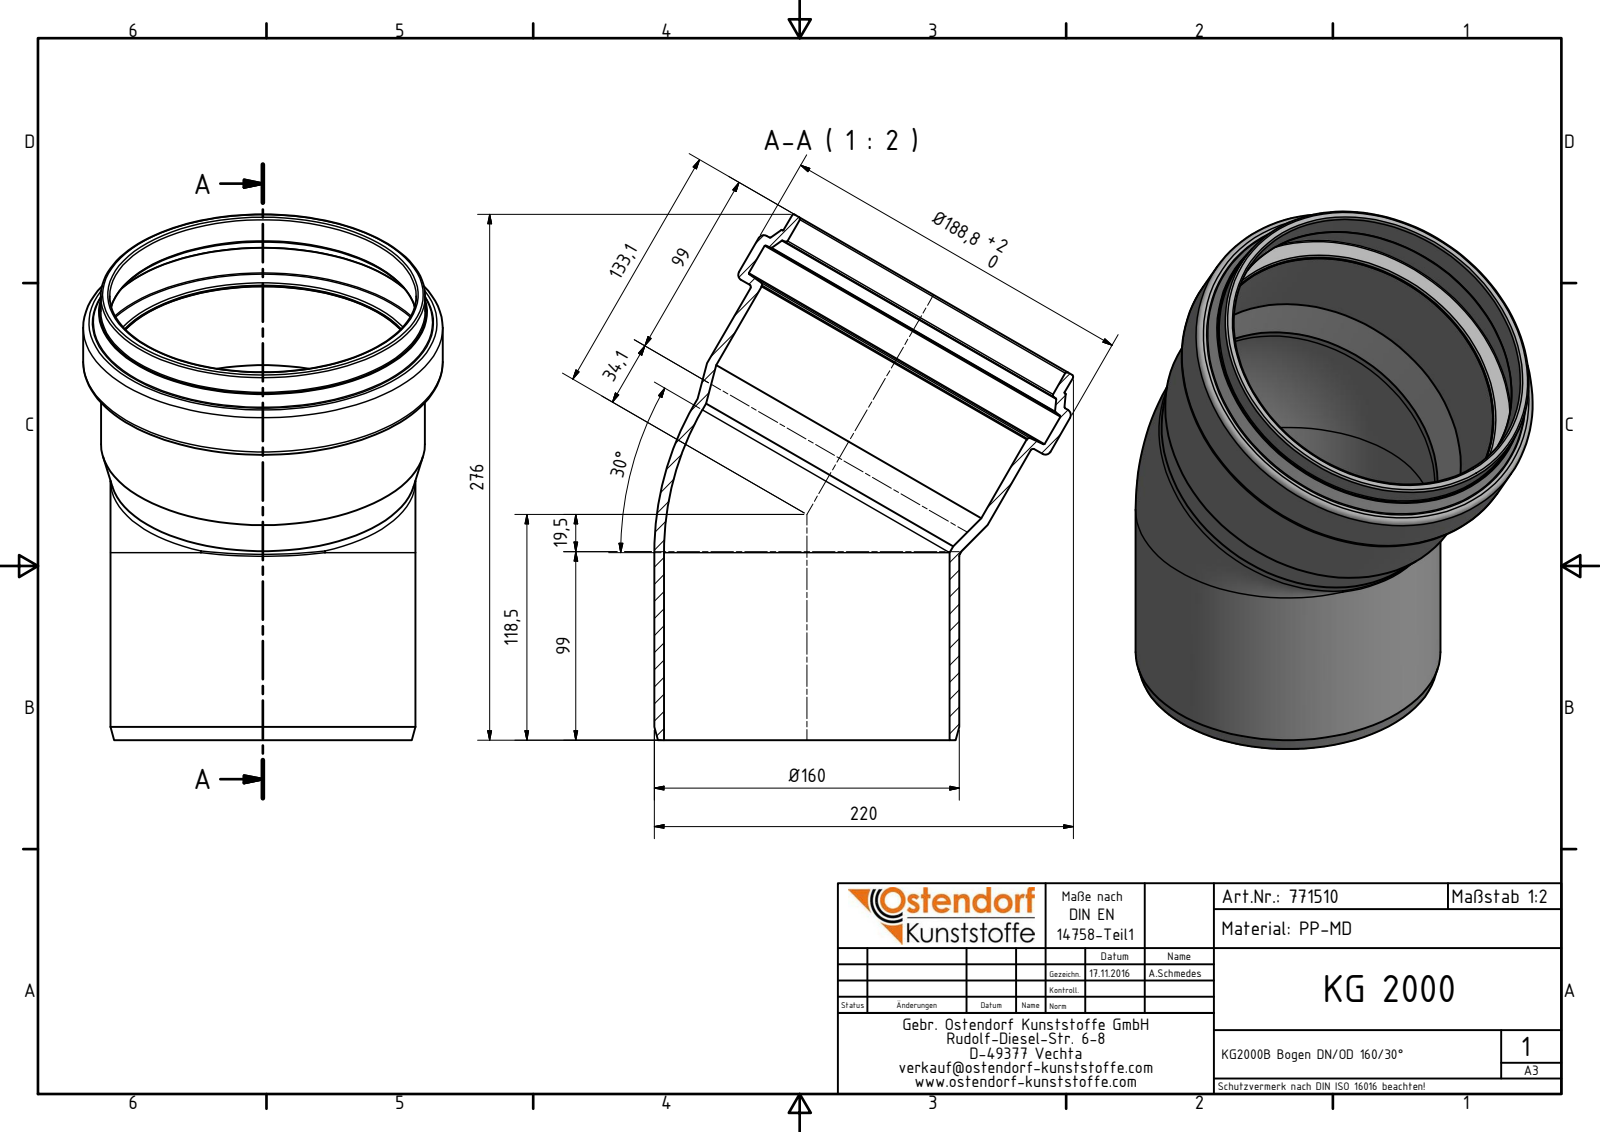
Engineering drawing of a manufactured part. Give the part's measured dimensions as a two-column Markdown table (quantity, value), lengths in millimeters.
| quantity | value |
| --- | --- |
| part name | 771510 KG2000B Bogen DN_OD 160_30° |
| STEP written by | Autodesk Inventor 2016 (AUTOMOTIVE_DESIGN) |
| units | millimeters |
| bodies | 1 solid, 42 faces (6 planar, 11 cylindrical, 25 other) |
| overall size | 276 × 220 × 188.8 |
| volume | 636 358 mm³ |
| surface area | 272 524 mm² |
| round holes (diameter × count) | 149.9 × 2, 160.7 × 1, 161 × 1, 179.4 × 1 |
| round bosses / shafts (diameter × count) | 160.1 × 2, 188.8 × 1, 170.4 × 1, 170.1 × 1 |
| main face-to-face distances | 43.7, 26.7, 17, 33.4, 6.7, 10.3, 2.44, 24.26, 30.96, 41.26 |
